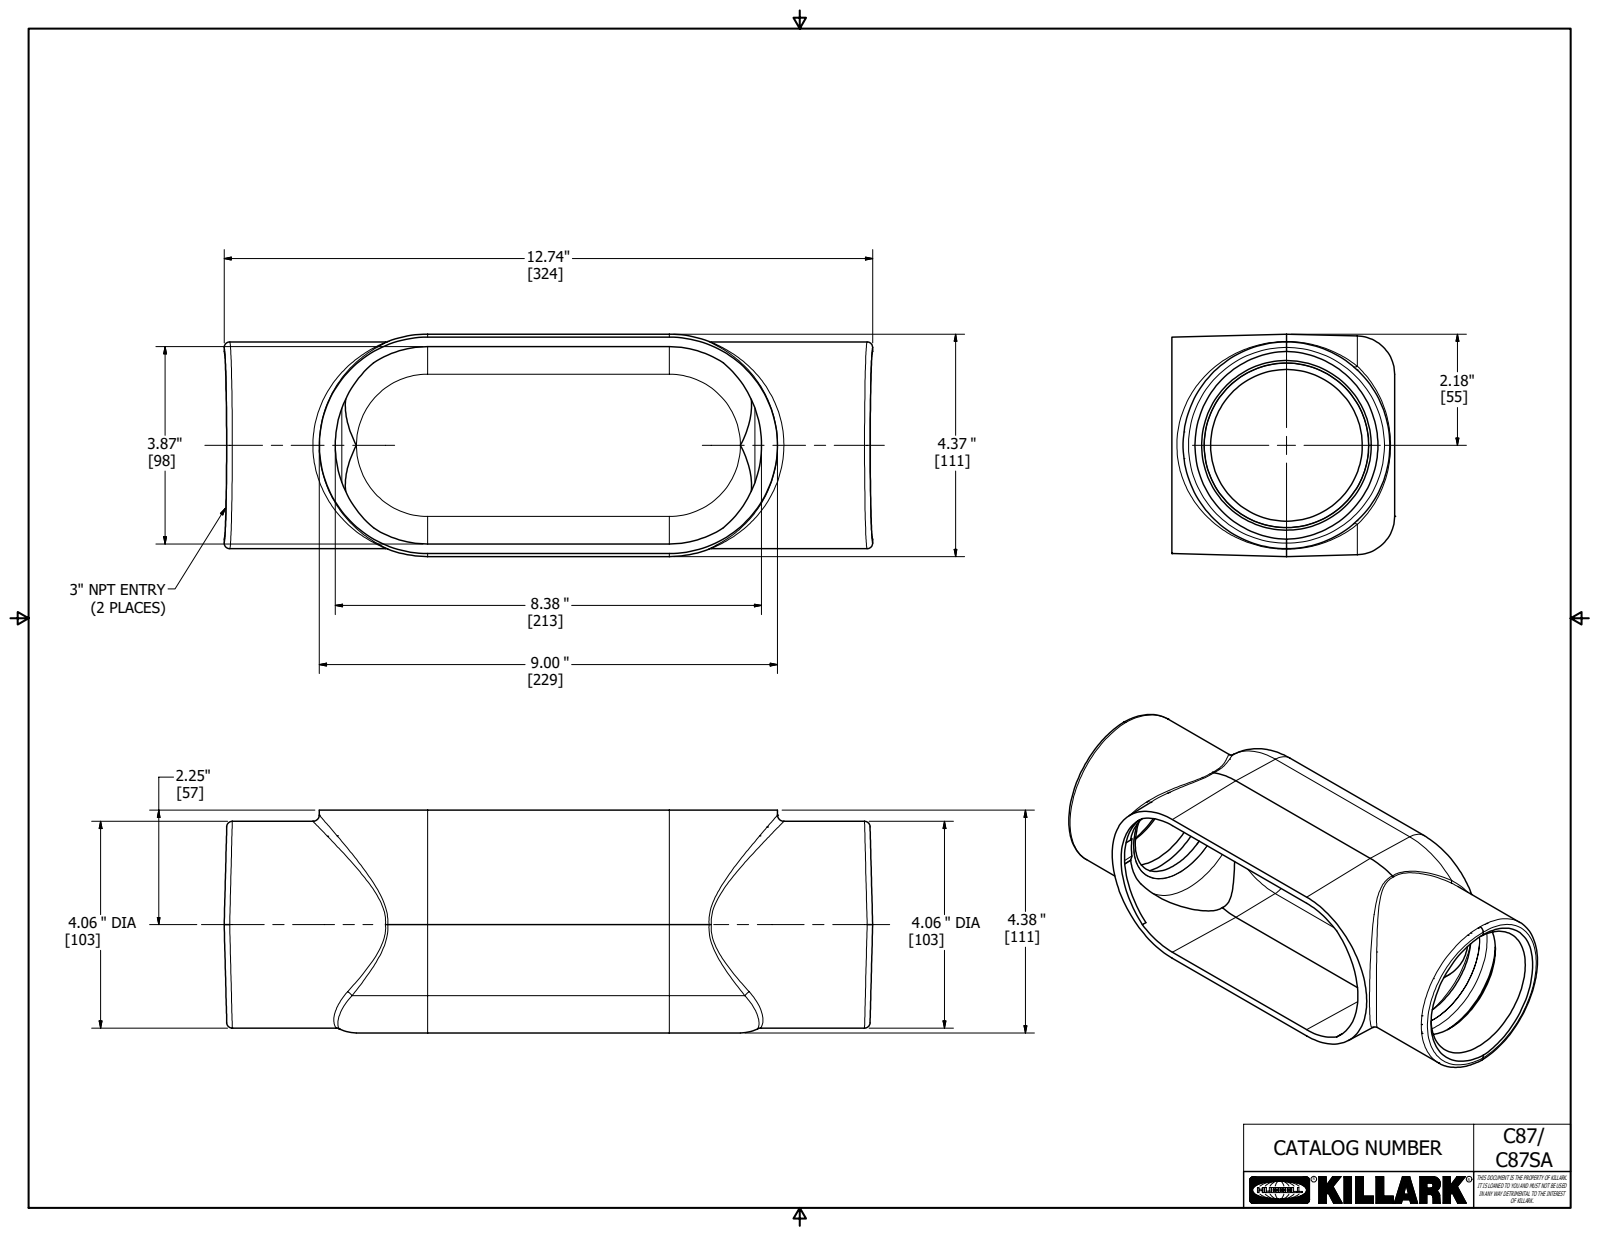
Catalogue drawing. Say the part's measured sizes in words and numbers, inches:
The part is named "17721". Its 3-D file was written by "Autodesk Inventor 2018 (AUTOMOTIVE_DESIGN)". It is 1 solid with 96 faces: 32 planar, 18 cylindrical and 46 other. Overall it measures 12.743 by 4.375 by 4.368 inches. Its volume is 36.1 cubic inches and its surface area 327.3 square inches. Round holes: 1 of diameter 3.511, 1 of diameter 3.875. Round bosses or shafts: 1 of diameter 4.062. Partial cylindrical surfaces (rounded edges, fillets, slot ends): 4 of radius 0.05, 4 of radius 0.125, 2 of radius 0.562, 2 of radius 0.75. The main face-to-face distances are 0.187, 4.18, 4.368, 3.993, 4.375, 4.187, 0.031, 0.156, 4.344, 12.743.
